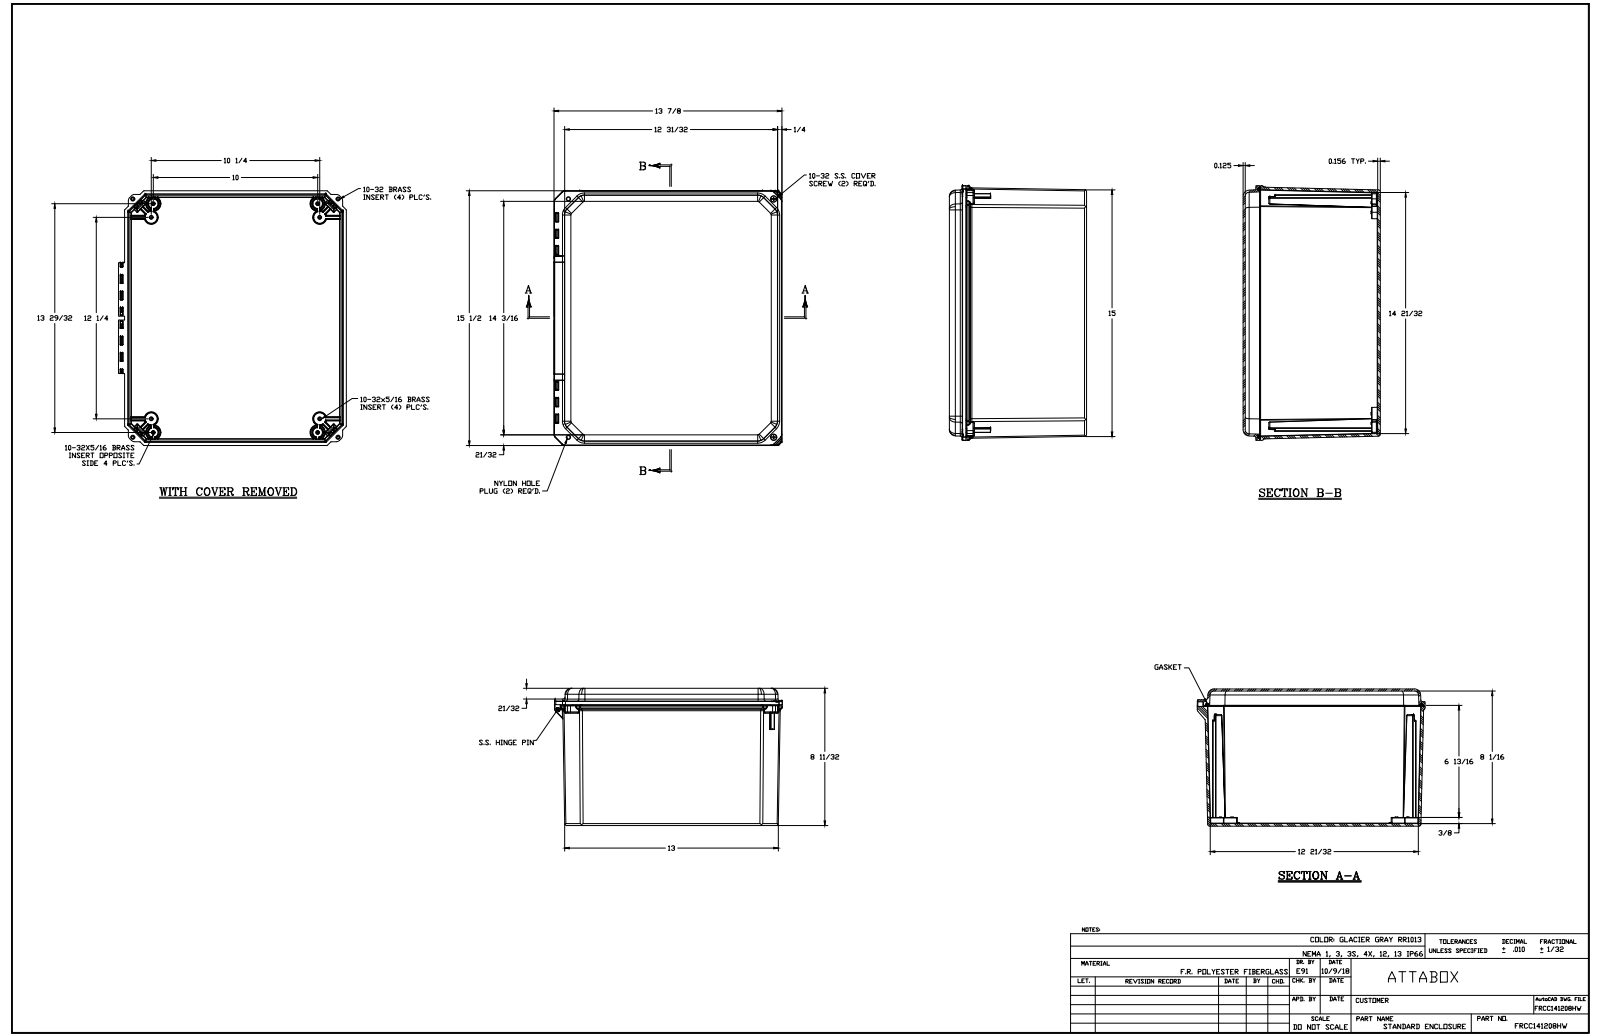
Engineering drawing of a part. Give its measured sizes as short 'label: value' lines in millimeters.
name: FRCC141208HW
written by: SolidWorks 2018 (AUTOMOTIVE_DESIGN)
unit: mm
bodies: 23 solids, 2119 faces (603 planar, 800 cylindrical, 716 other)
size: 393.6 × 352.2 × 211.9
volume: 2 189 000 mm³; area: 1 152 000 mm²
holes: 12× ⌀4, 8× ⌀3.9, 4× ⌀5.6, 4× ⌀6.4, 4× ⌀7.9, 2× ⌀3.8, 1× ⌀3.5
bosses: 12× ⌀6.2, 2× ⌀11.4, 2× ⌀5.3, 2× ⌀5.1, 1× ⌀3.4
rounds: 202× R0.3, 116× R0.1, 59× R0.5, 38× R0.8, 29× R3.2, 24× R0.8, 24× R2.3, 24× R6.4
face distances: 3.2, 4, 207.9, 208.7, 204.8, 211.9, 4.1, 4, 186.5, 25.4
hole spacings: 290.2, 21, 32.5, 40.2, 258, 285.7, 332, 340.8
